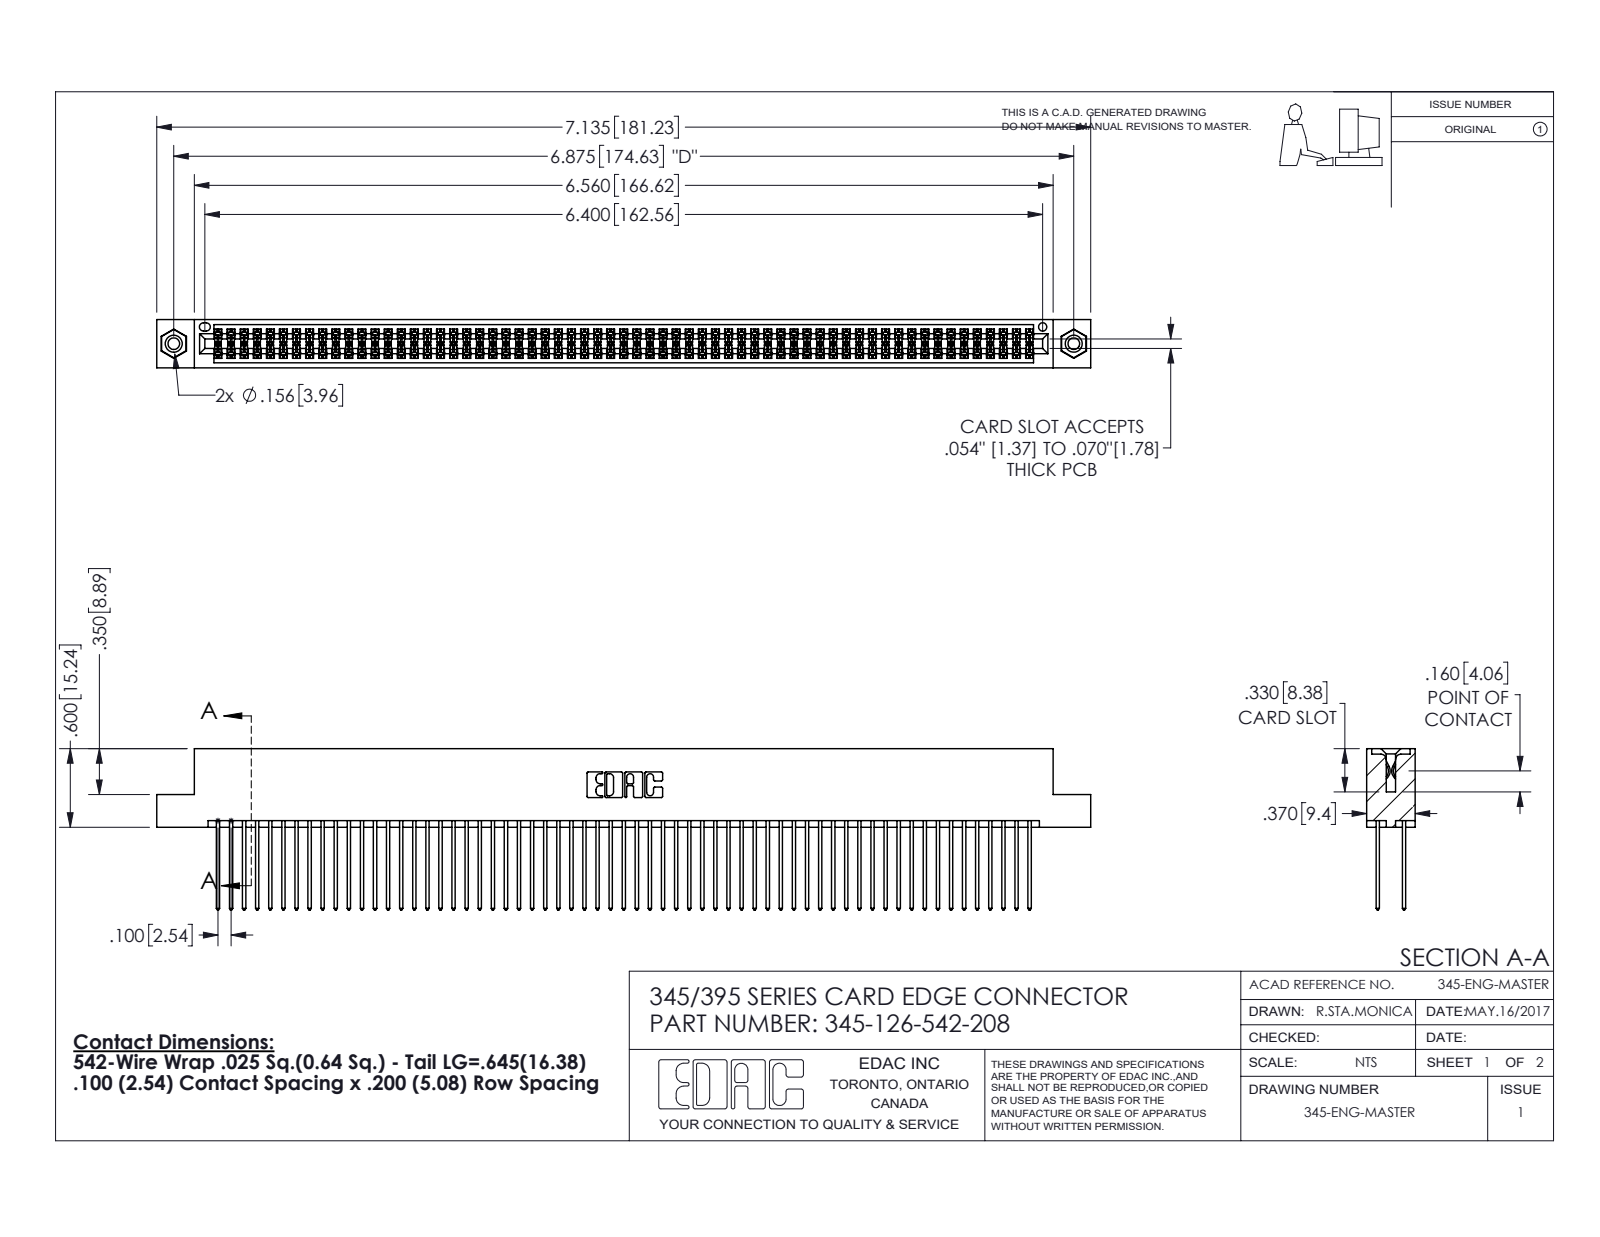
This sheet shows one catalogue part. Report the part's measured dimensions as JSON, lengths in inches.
{"part_name": "345-292-001_345-293-142; 345 Part_Flush Mounting Lugs - 0.156 Dia-TI; 345-126-542-208; 345-250-001_345-250-003-102", "step_written_by": "SolidWorks 2016 (CONFIG_CONTROL_DESIGN)", "units": "inches", "bodies": {"solids": 129, "faces": 6486, "planar": 4270, "cylindrical": 2200, "other": 16}, "overall_size": [7.135, 1.232, 0.37], "volume_in3": 1.122, "surface_area_in2": 47.02, "round_holes": [[0.089, 2], [0.125, 2], [0.156, 2], [0.064, 1]], "round_bosses_or_shafts": [[0.155, 2]], "partial_cylinders_radius": [[0.006, 189], [0.01, 126], [0.01, 22], [0.007, 6], [0.031, 6], [0.026, 3], [0.014, 2], [0.019, 2]], "face_to_face_distances": [0.072, 0.298, 0.2, 0.098, 0.272, 0.025, 0.225, 0.37, 0.175, 0.149], "hole_center_spacings": [0.27, 6.639, 6.875]}
